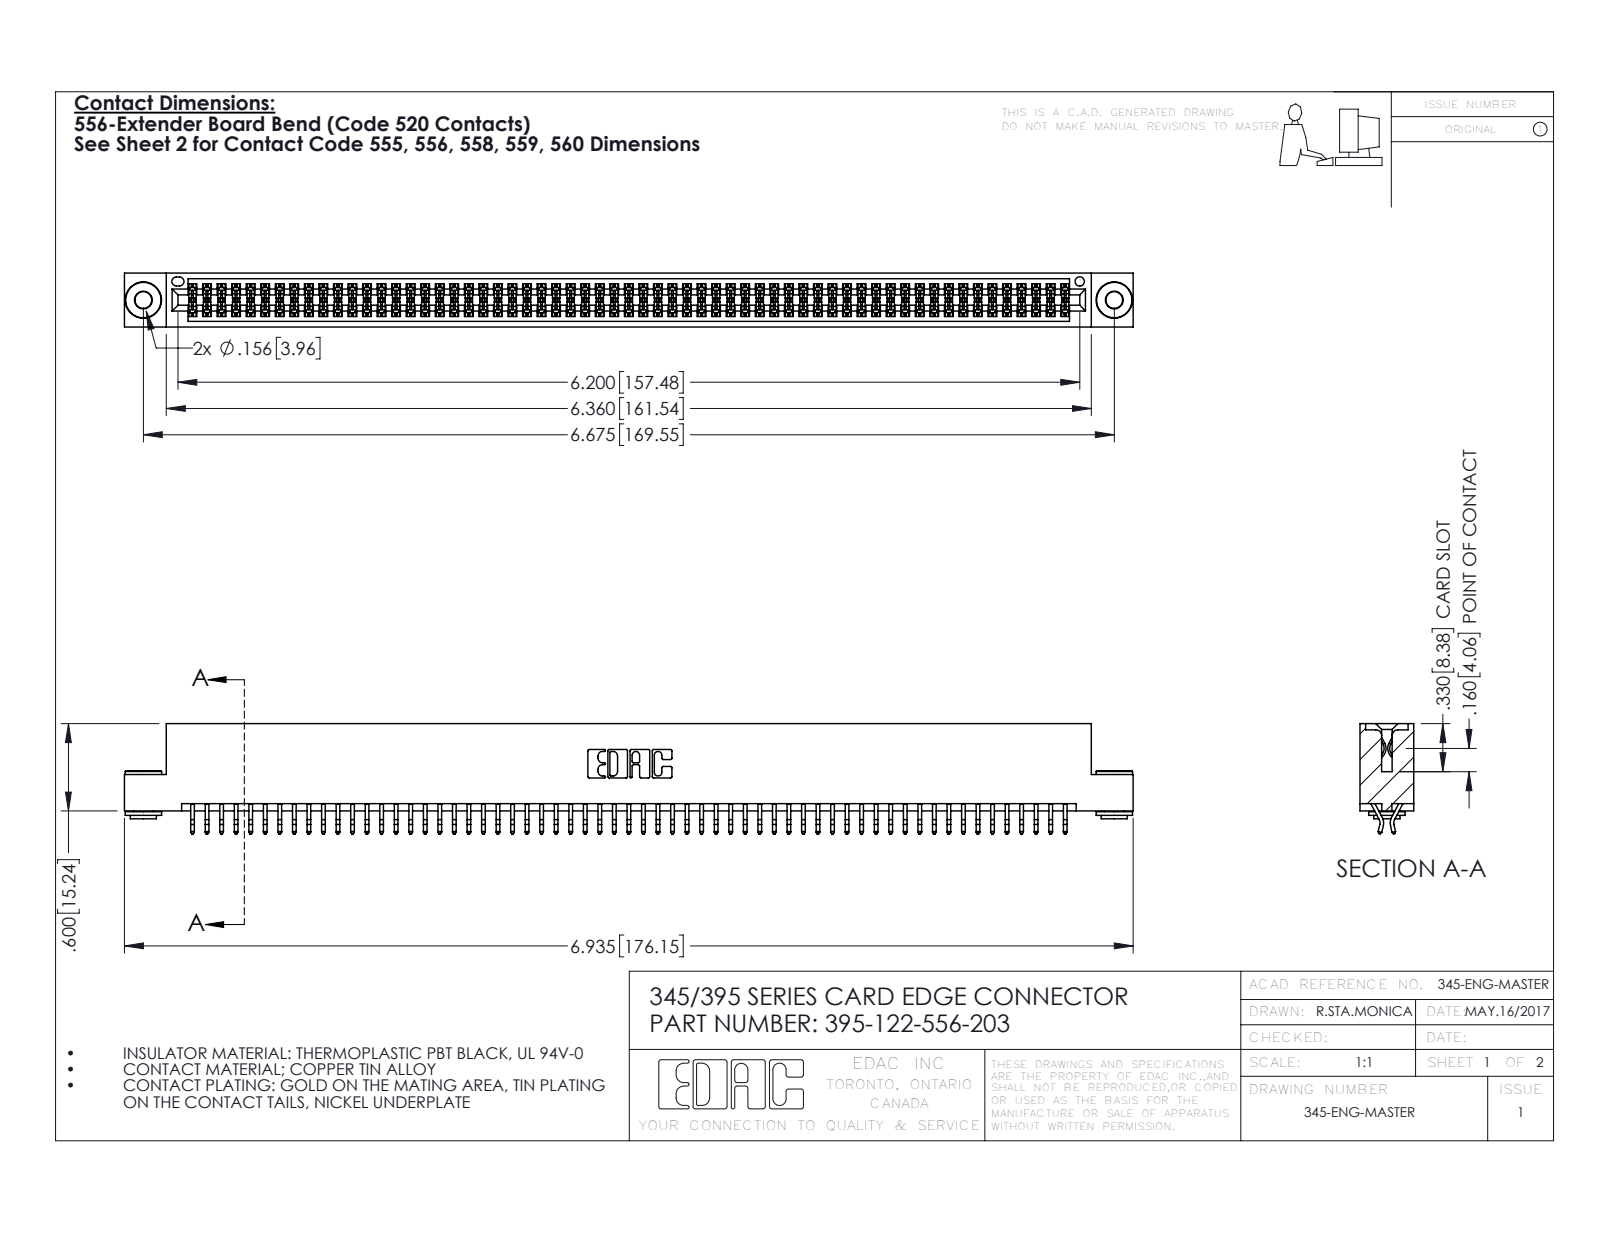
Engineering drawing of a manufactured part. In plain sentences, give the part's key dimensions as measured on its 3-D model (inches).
The part is named "395-122-556-203; 345-292-001_556 Tail; 345 Part_Flush Mounting Lugs - 0.156 Dia-TH; 345-250-002_345-250-002-102". Its 3-D file was written by "SolidWorks 2016 (CONFIG_CONTROL_DESIGN)". It is 125 solids with 6996 faces: 4604 planar, 2384 cylindrical and 8 other. Overall it measures 6.935 by 0.757 by 0.37 inches. Its volume is 1.056 cubic inches and its surface area 40.36 square inches. Round holes: 2 of diameter 0.116, 2 of diameter 0.156, 1 of diameter 0.064. Round bosses or shafts: 2 of diameter 0.25, 2 of diameter 0.18, 2 of diameter 0.136. Partial cylindrical surfaces (rounded edges, fillets, slot ends): 183 of radius 0.006, 22 of radius 0.01, 6 of radius 0.007, 6 of radius 0.031, 3 of radius 0.026, 2 of radius 0.01, 2 of radius 0.014, 2 of radius 0.019. The main face-to-face distances are 0.072, 0.298, 0.37, 0.2, 0.025, 0.098, 0.272, 0.225, 0.175, 0.149. The hole center spacings are 0.27, 6.439, 6.675.
